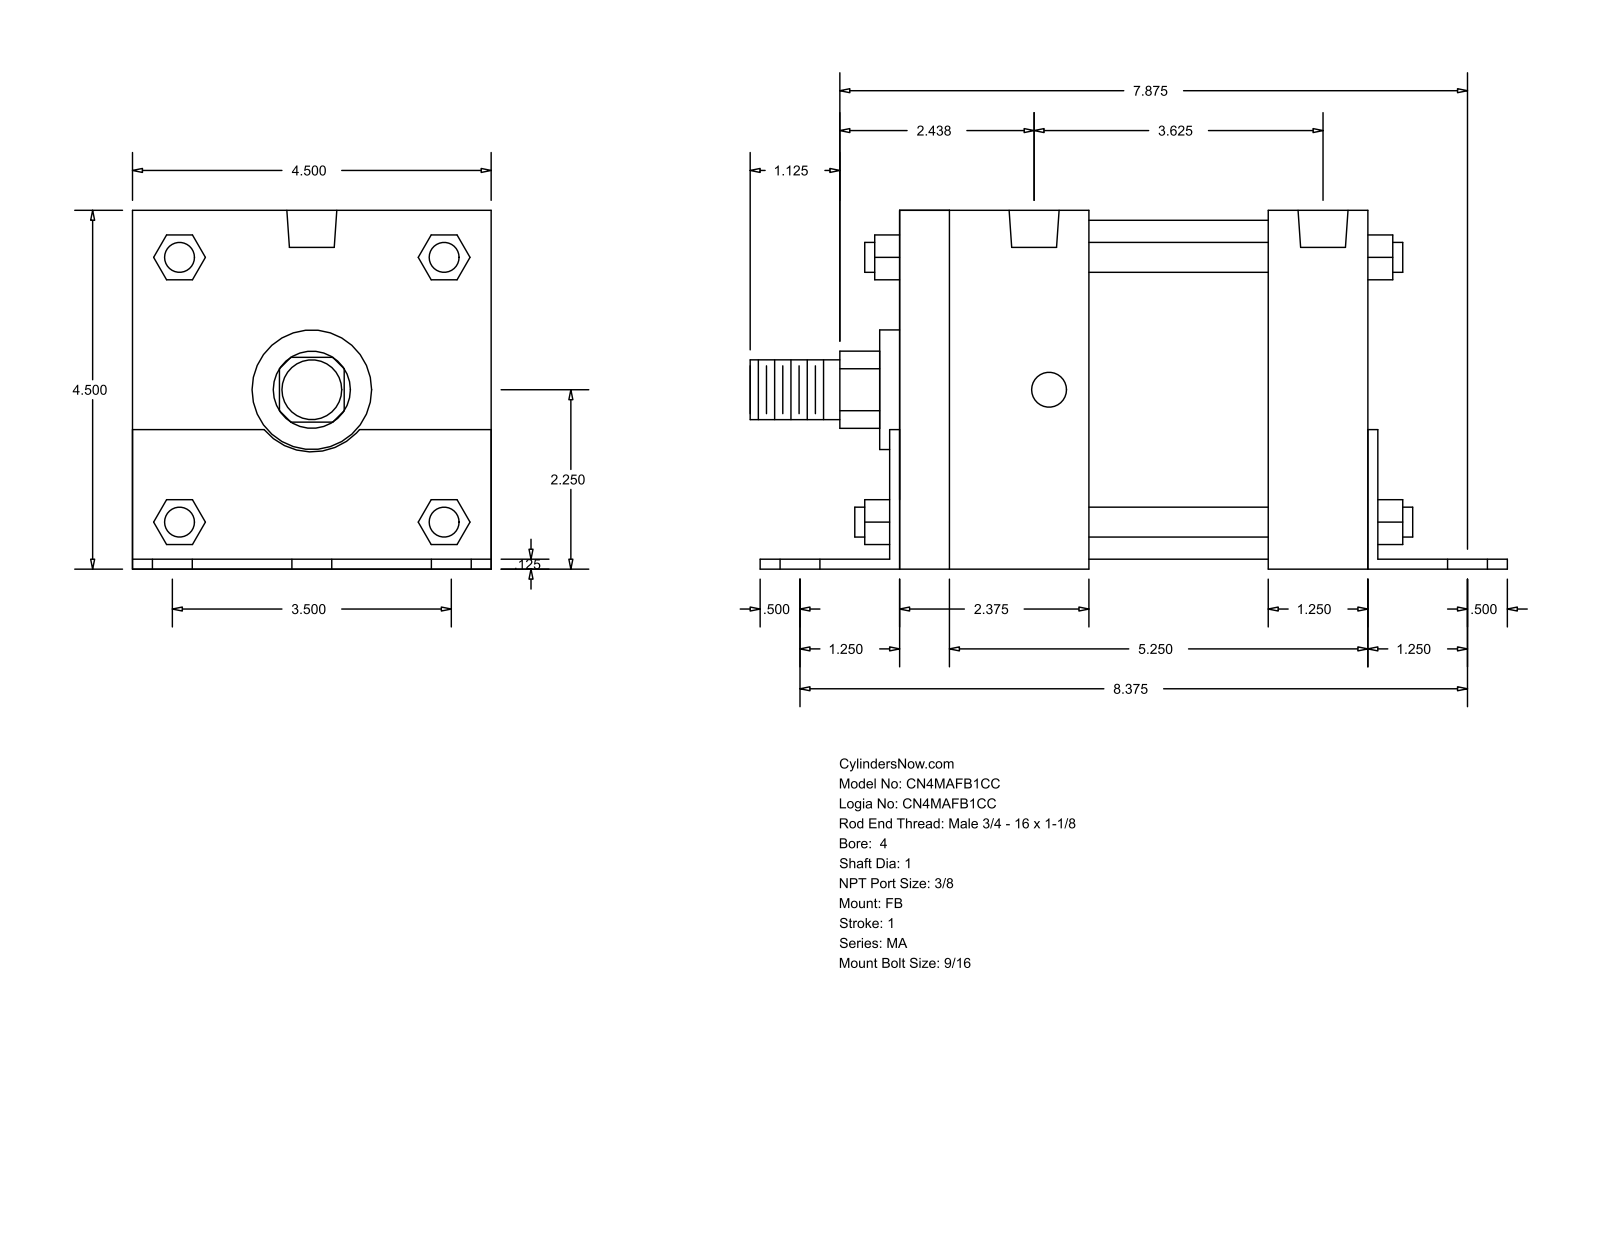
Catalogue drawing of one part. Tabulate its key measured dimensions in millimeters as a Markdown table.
| quantity | value |
| --- | --- |
| part name | MA_FB__0400_1 |
| STEP written by | GSSL Pune (CONFIG_CONTROL_DESIGN) |
| units | millimeters |
| bodies | 0 solids, 140 faces (105 planar, 35 cylindrical, 0 other) |
| overall size | 241.3 × 114.35 × 114.3 |
| round holes (diameter × count) | 14.29 × 6, 11.11 × 4, 15.93 × 2 |
| round bosses / shafts (diameter × count) | 9.53 × 4, 107.95 × 1, 38.1 × 1, 25.4 × 1, 19.05 × 1 |
| partial cylindrical surfaces (radius × count) | 12.29 × 1, 19.81 × 1 |
| main face-to-face distances | 114.3, 3.17, 114.35, 152.4, 3.12, 111.18, 149.23, 155.57, 120.65, 117.48 |
| hole center spacings | 44.45, 217.32, 212.73, 64, 67.51, 82.55, 86.85, 88.9 |
